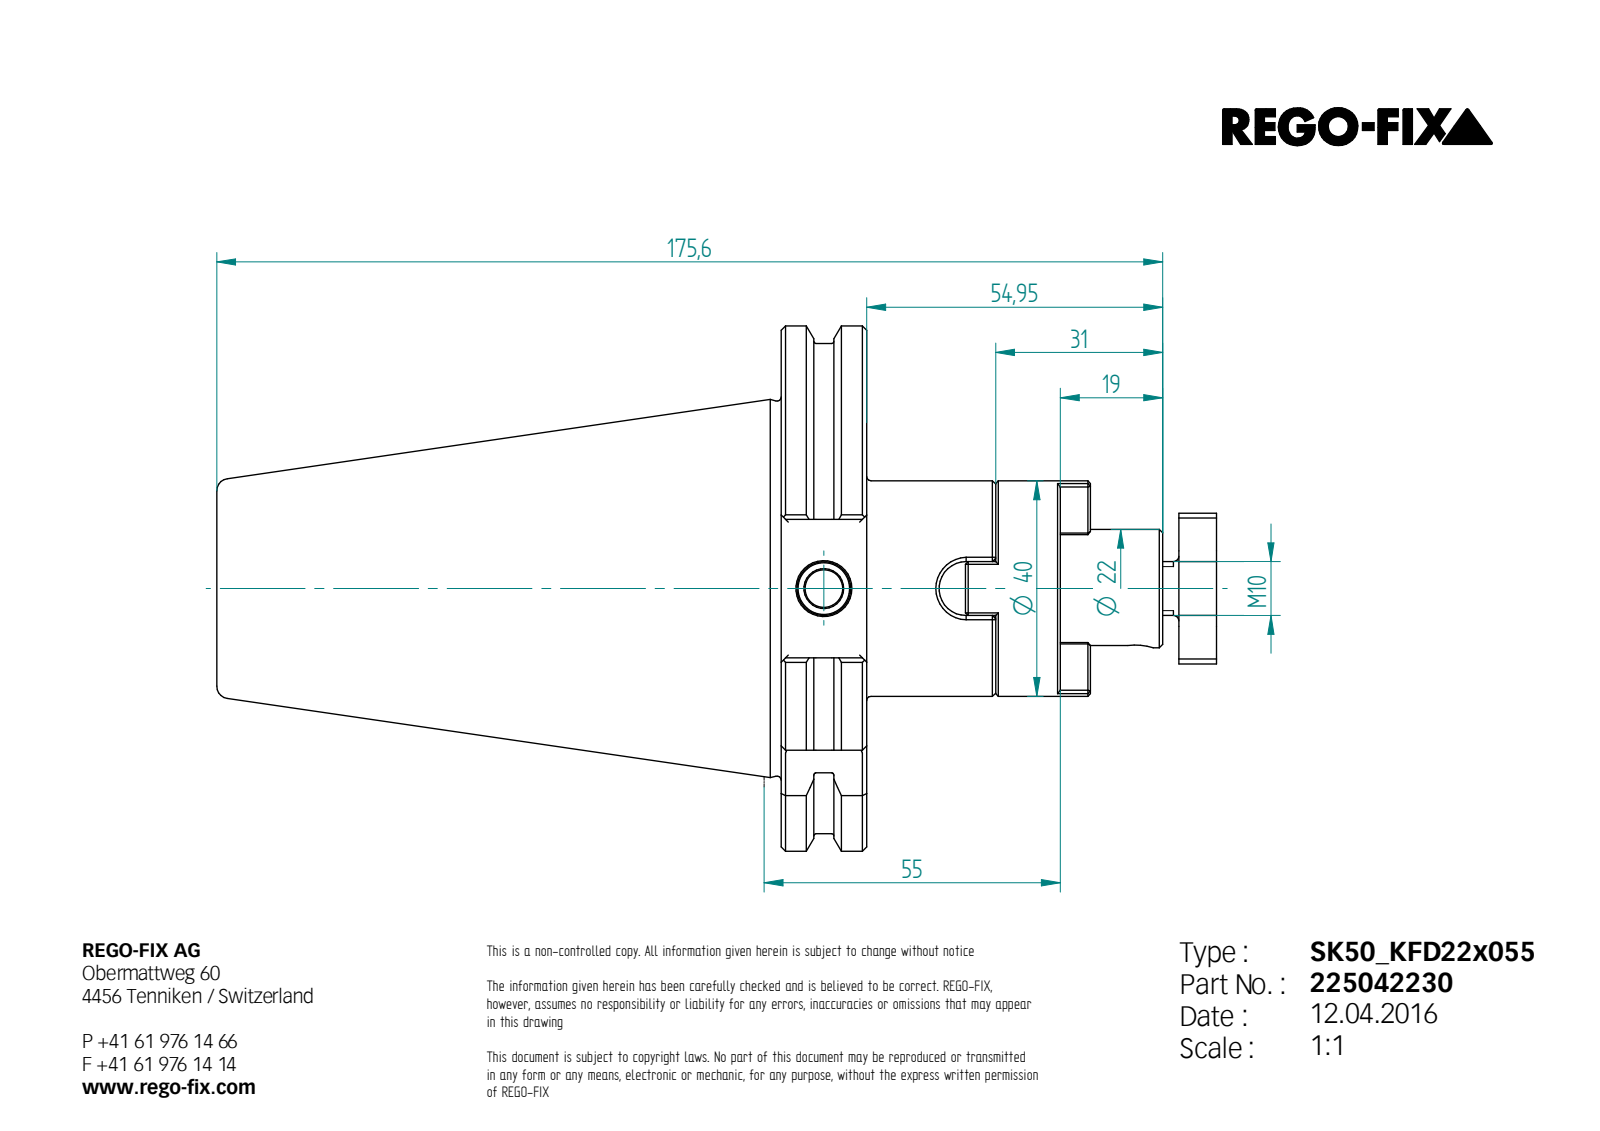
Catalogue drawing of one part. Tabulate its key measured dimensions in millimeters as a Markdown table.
| quantity | value |
| --- | --- |
| STEP written by | Unknown (AUTOMOTIVE_DESIGN) |
| units | millimeters |
| bodies | 3 solids, 232 faces (131 planar, 40 cylindrical, 61 other) |
| overall size | 185.6 × 97.5 × 93.58 |
| volume | 373 935 mm³ |
| surface area | 57 382 mm² |
| round holes (diameter × count) | 7 × 1, 8.38 × 1, 10 × 1, 10.5 × 1, 20.75 × 1, 22 × 1, 25 × 1 |
| round bosses / shafts (diameter × count) | 91 × 1, 40 × 1, 21.4 × 1, 10 × 1 |
| partial cylindrical surfaces (radius × count) | 0.5 × 5, 2 × 4, 3 × 2, 5 × 1, 14 × 1, 48.75 × 1 |
| main face-to-face distances | 15.85, 39.8, 23.95, 51.8, 35.95, 12, 10, 7.85, 17.85, 80.8 |
